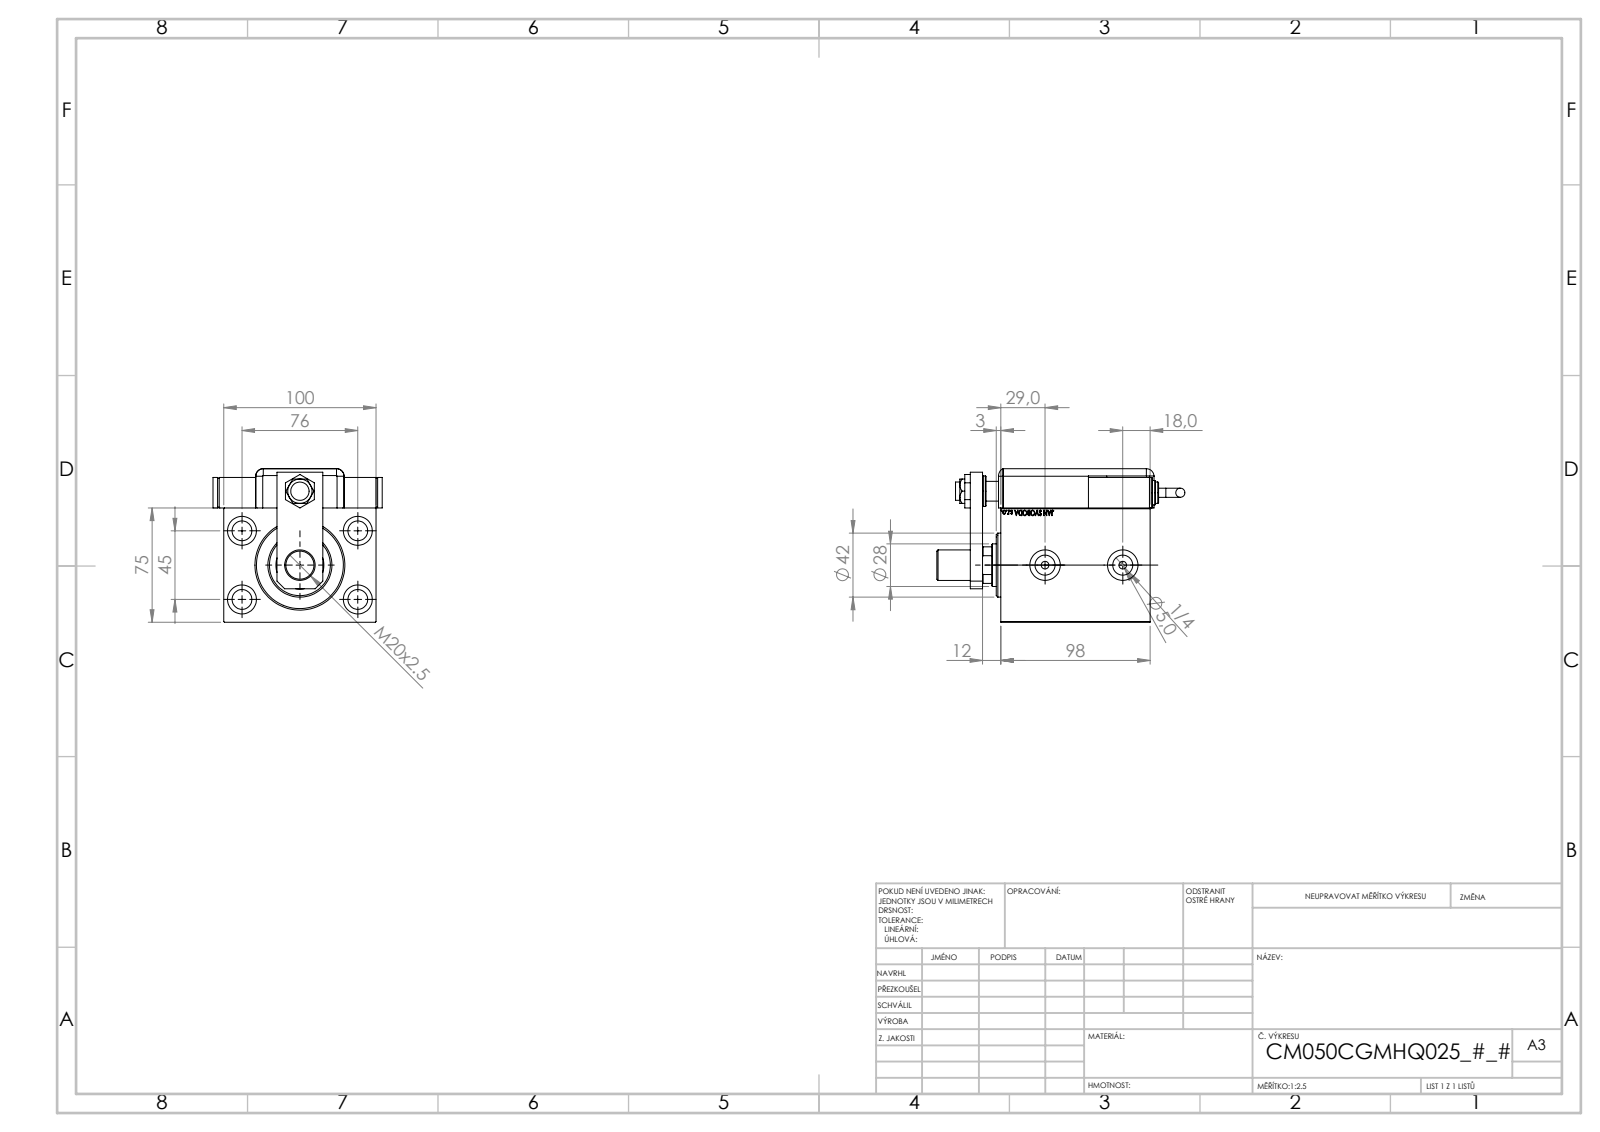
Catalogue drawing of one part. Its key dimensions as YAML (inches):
part_name: "SWITCH_Q_FRONT_BACK; NUT_D19; SWITCH DIM A_G; ZARAZKA_Q (+7 more)"
step_written_by: "SolidWorks 2019 (CONFIG_CONTROL_DESIGN)"
units: inches
bodies: {solids: 14, faces: 1263, planar: 619, cylindrical: 121, other: 523}
overall_size: [6.408, 4.37, 3.969]
volume: 47.71
surface_area: 256.9
round_holes:
  - {diameter: 0.512, count: 5}
  - {diameter: 0.748, count: 4}
  - {diameter: 0.787, count: 3}
  - {diameter: 0.157, count: 2}
  - {diameter: 0.197, count: 2}
  - {diameter: 0.315, count: 2}
  - {diameter: 0.518, count: 2}
  - {diameter: 0.472, count: 1}
  - {diameter: 0.551, count: 1}
  - {diameter: 0.728, count: 1}
  - {diameter: 1.102, count: 1}
  - {diameter: 1.24, count: 1}
round_bosses_or_shafts:
  - {diameter: 0.787, count: 3}
  - {diameter: 0.63, count: 2}
  - {diameter: 0.551, count: 2}
  - {diameter: 0.236, count: 2}
  - {diameter: 1.654, count: 1}
  - {diameter: 0.709, count: 1}
partial_cylinders:
  - {radius: 0.197, count: 9}
  - {radius: 0.394, count: 1}
  - {radius: 0.531, count: 1}
face_to_face_distances: [2.953, 0.118, 3.937, 3.858, 0.551, 0.787, 0.11, 3.307, 1.016, 3.969]
hole_center_spacings: [1.739, 1.772, 1.813, 2.992, 3.17, 3.477, 0.787, 1.909]
